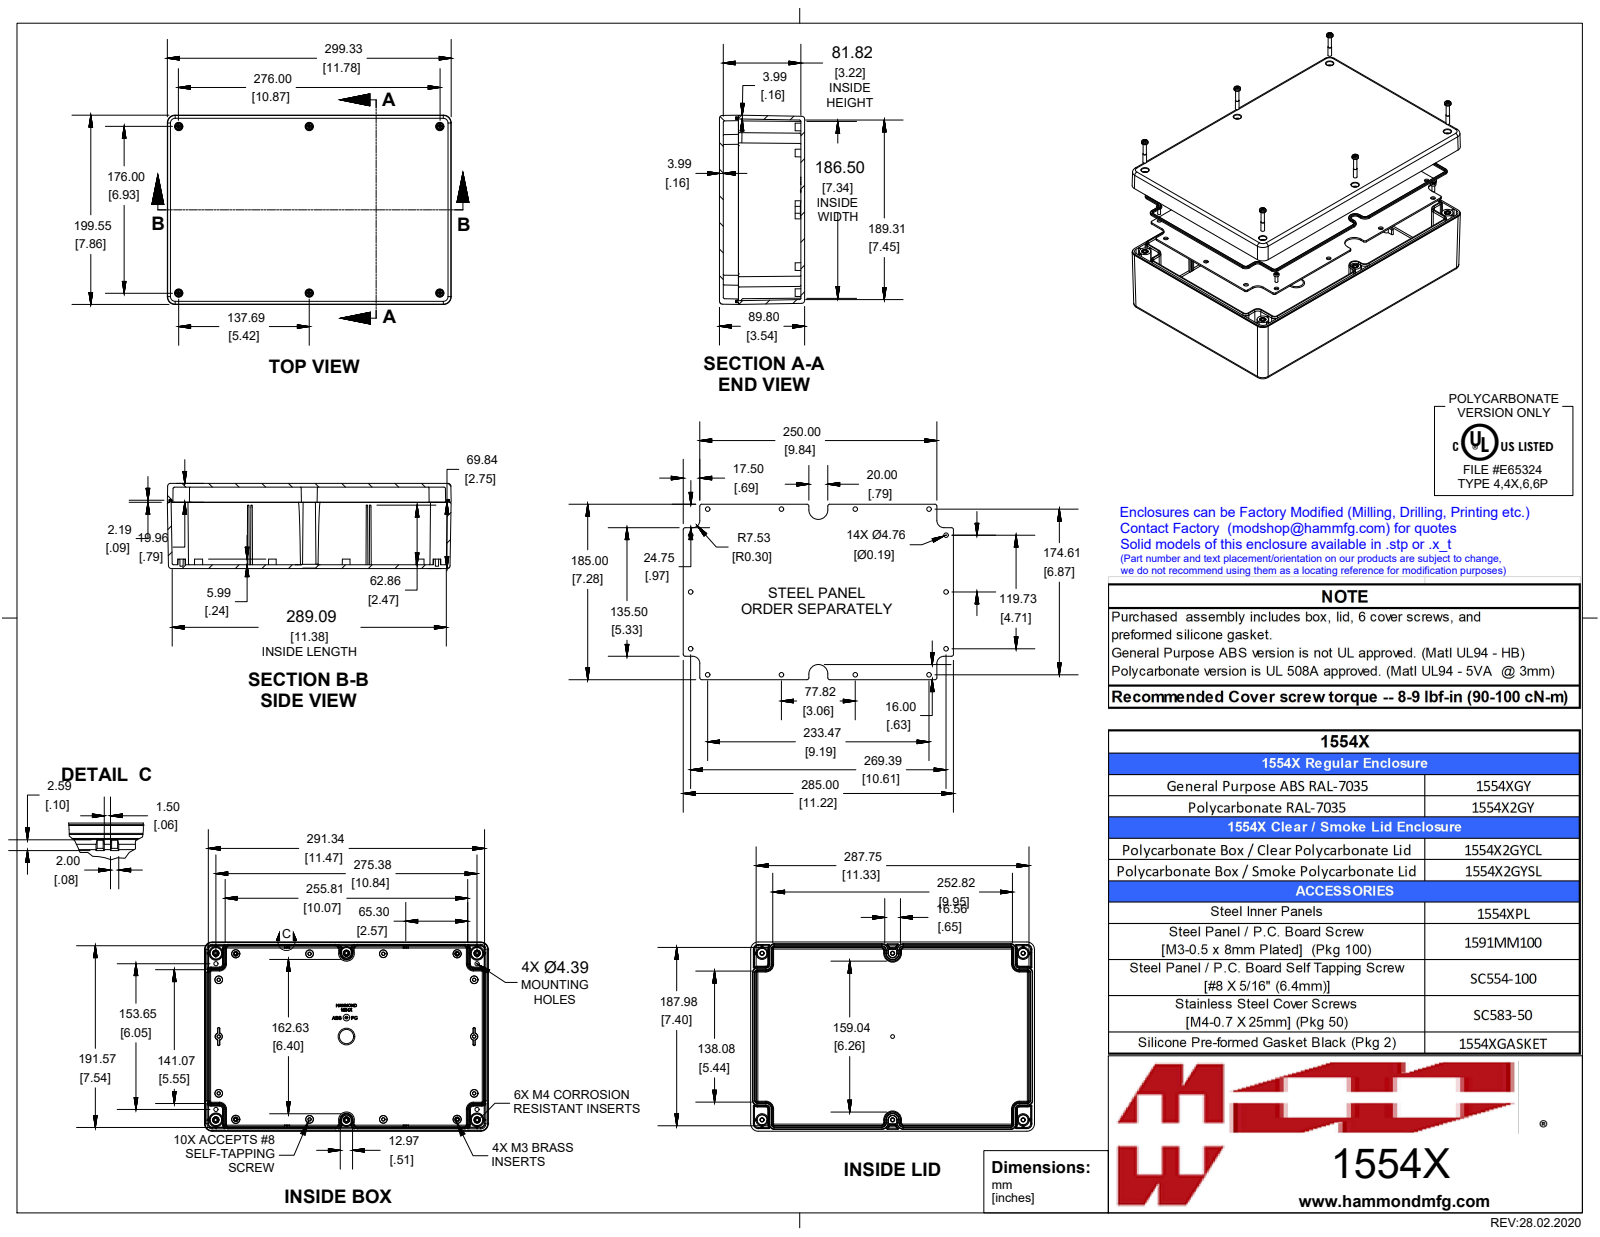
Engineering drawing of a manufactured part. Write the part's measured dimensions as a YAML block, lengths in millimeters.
part_name: "1554XGY"
step_written_by: "SolidWorks 2019 (AUTOMOTIVE_DESIGN)"
units: millimeters
bodies: {solids: 24, faces: 3237, planar: 921, cylindrical: 732, other: 1584}
overall_size: [300, 200, 90]
volume: 956300
surface_area: 590600
round_holes:
  - {diameter: 4.7, count: 14}
  - {diameter: 3.3, count: 6}
  - {diameter: 3.6, count: 6}
  - {diameter: 2.5, count: 4}
  - {diameter: 7, count: 1}
round_bosses_or_shafts:
  - {diameter: 6.9, count: 6}
  - {diameter: 6.4, count: 6}
  - {diameter: 5.4, count: 6}
  - {diameter: 5.3, count: 6}
  - {diameter: 3.9, count: 6}
  - {diameter: 3.5, count: 6}
  - {diameter: 3, count: 5}
  - {diameter: 4.8, count: 4}
partial_cylinders:
  - {radius: 0.5, count: 34}
  - {radius: 0.3, count: 20}
  - {radius: 2, count: 14}
  - {radius: 0.8, count: 12}
  - {radius: 3, count: 12}
  - {radius: 1, count: 10}
  - {radius: 0.7, count: 8}
  - {radius: 8, count: 8}
face_to_face_distances: [4, 86, 90, 82, 6, 10, 76, 80, 1.6, 11.6]
hole_center_spacings: [78, 191.6, 21, 28.2, 32.9, 39, 60, 88.1]
